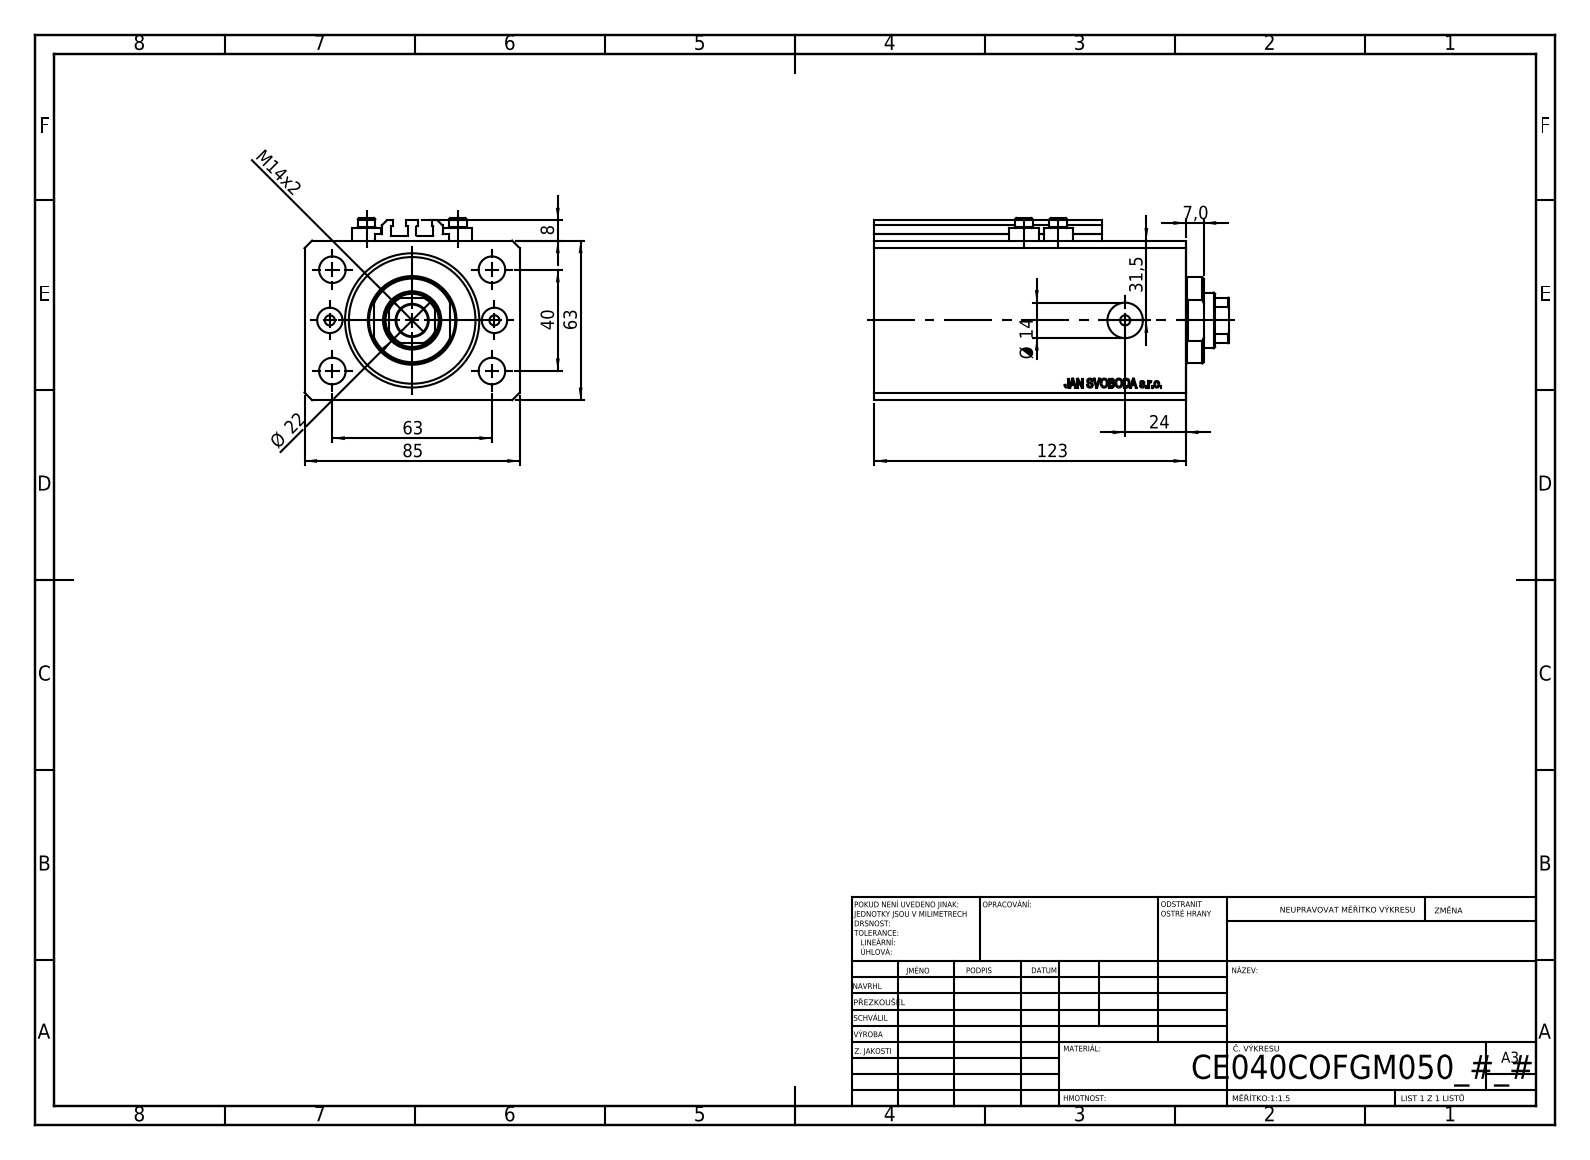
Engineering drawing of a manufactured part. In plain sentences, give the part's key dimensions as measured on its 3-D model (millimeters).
The part is named "V250CE_VC_C; ALLEN BOLT V250CE; V250CE_C_Body; V250CE_C_VCP". Its 3-D file was written by "SolidWorks 2019 (CONFIG_CONTROL_DESIGN)". It is 8 solids with 1034 faces: 504 planar, 86 cylindrical and 444 other. Overall it measures 140 by 85 by 72 millimeters. Its volume is 587 344 cubic millimeters and its surface area 113 688 square millimeters. Round holes: 8 of diameter 4, 4 of diameter 10.5, 2 of diameter 10, 2 of diameter 14, 1 of diameter 12.5, 1 of diameter 22, 1 of diameter 40, 1 of diameter 53. Round bosses or shafts: 4 of diameter 11.6, 4 of diameter 7, 1 of diameter 34. Partial cylindrical surfaces (rounded edges, fillets, slot ends): 10 of radius 0.2, 1 of radius 10.5. The main face-to-face distances are 63, 85, 123, 17, 106, 11.4, 94.6, 111.6, 2.5, 10. The hole center spacings are 20.02, 37.31, 67.05, 13.6, 32.5, 36, 38.48, 40.
